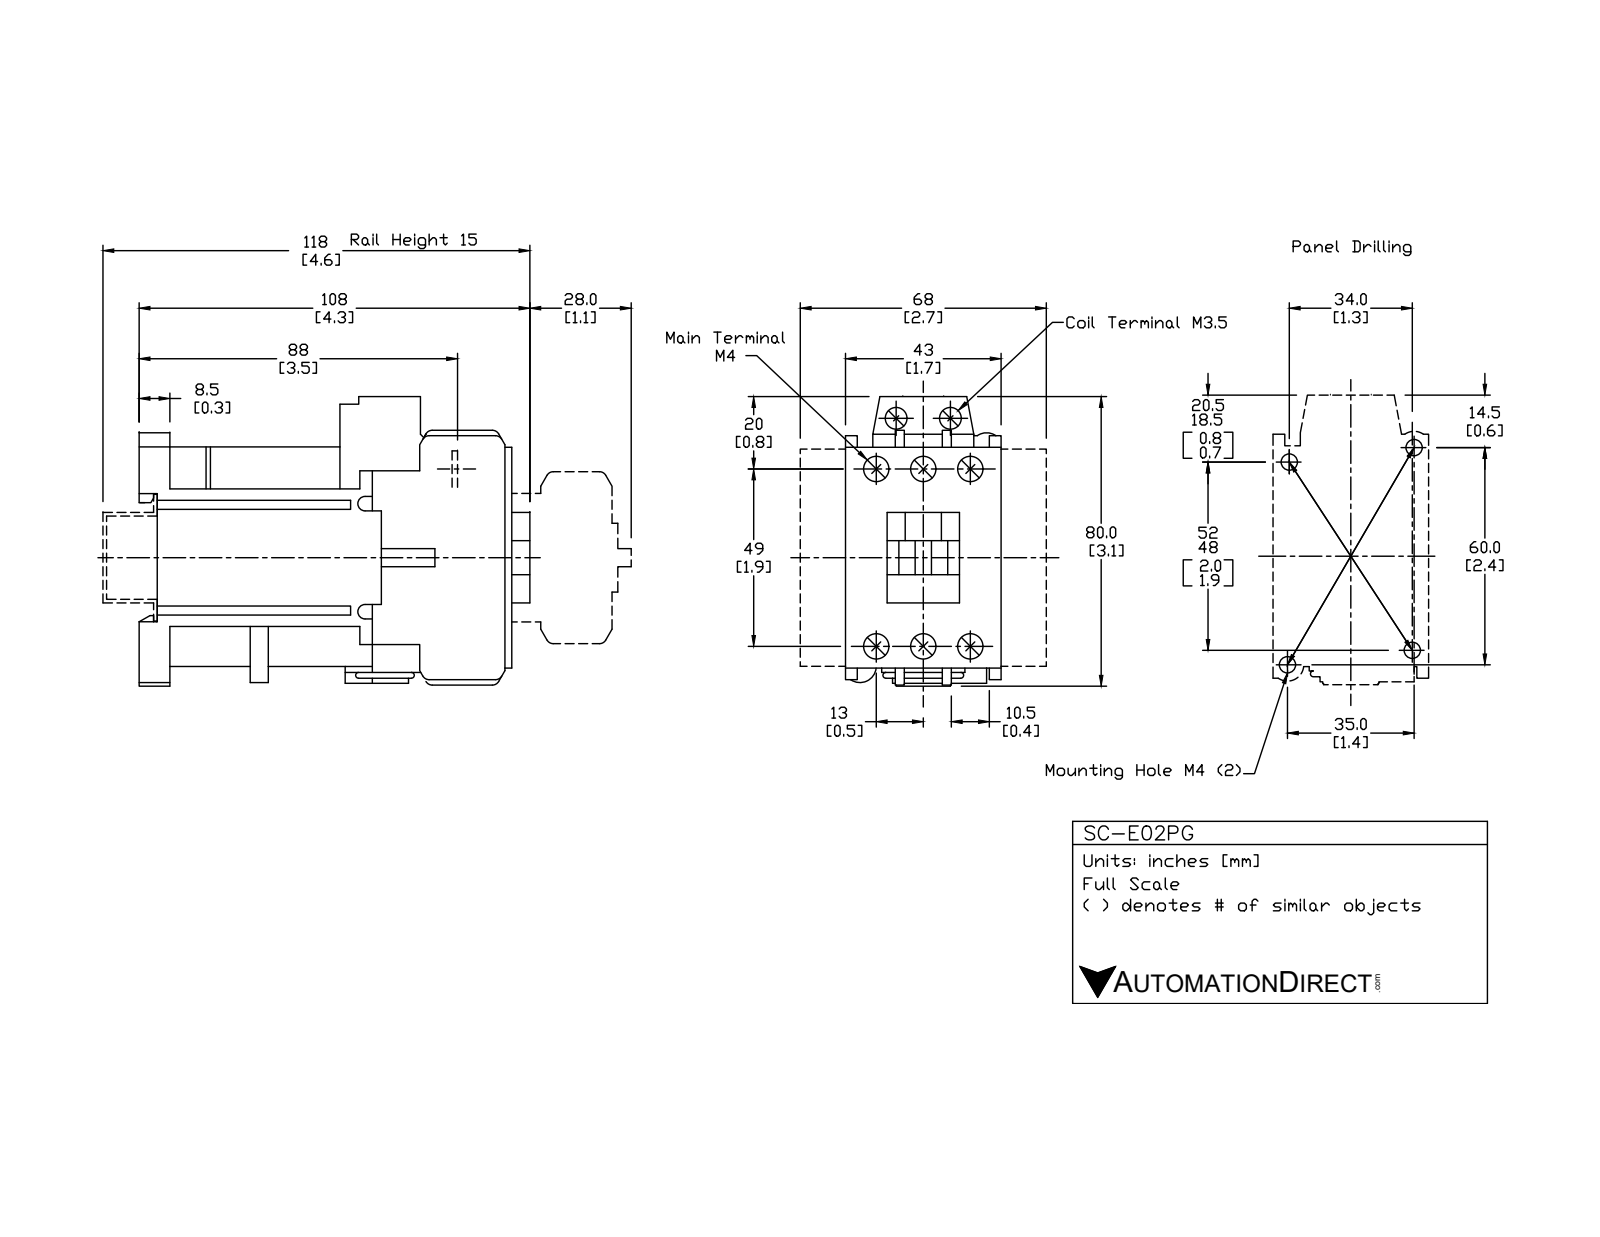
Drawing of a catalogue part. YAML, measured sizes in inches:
part_name: "SC-E02G-24VDC"
step_written_by: "SolidWorks 2015 (AUTOMOTIVE_DESIGN)"
units: inches
bodies: {solids: 32, faces: 1701, planar: 1440, cylindrical: 213, other: 48}
overall_size: [4.252, 3.22, 1.693]
volume: 13.95
surface_area: 94.1
round_holes:
  - {diameter: 0.157, count: 6}
  - {diameter: 0.161, count: 6}
  - {diameter: 0.276, count: 6}
  - {diameter: 0.138, count: 2}
  - {diameter: 0.142, count: 2}
  - {diameter: 0.189, count: 2}
  - {diameter: 0.264, count: 2}
  - {diameter: 0.063, count: 1}
round_bosses_or_shafts:
  - {diameter: 0.299, count: 6}
  - {diameter: 0.26, count: 2}
partial_cylinders:
  - {radius: 0.059, count: 32}
  - {radius: 0.02, count: 12}
  - {radius: 0.079, count: 11}
  - {radius: 0.039, count: 8}
  - {radius: 0.024, count: 4}
  - {radius: 0.118, count: 4}
  - {radius: 0.177, count: 4}
  - {radius: 0.134, count: 3}
face_to_face_distances: [1.693, 0.394, 0.65, 1.299, 0.138, 0.075, 0.256, 0.039, 0.02, 0.906]
hole_center_spacings: [0.512, 1.996, 1.929, 0.268, 0.298, 0.592, 0.625, 0.704]
